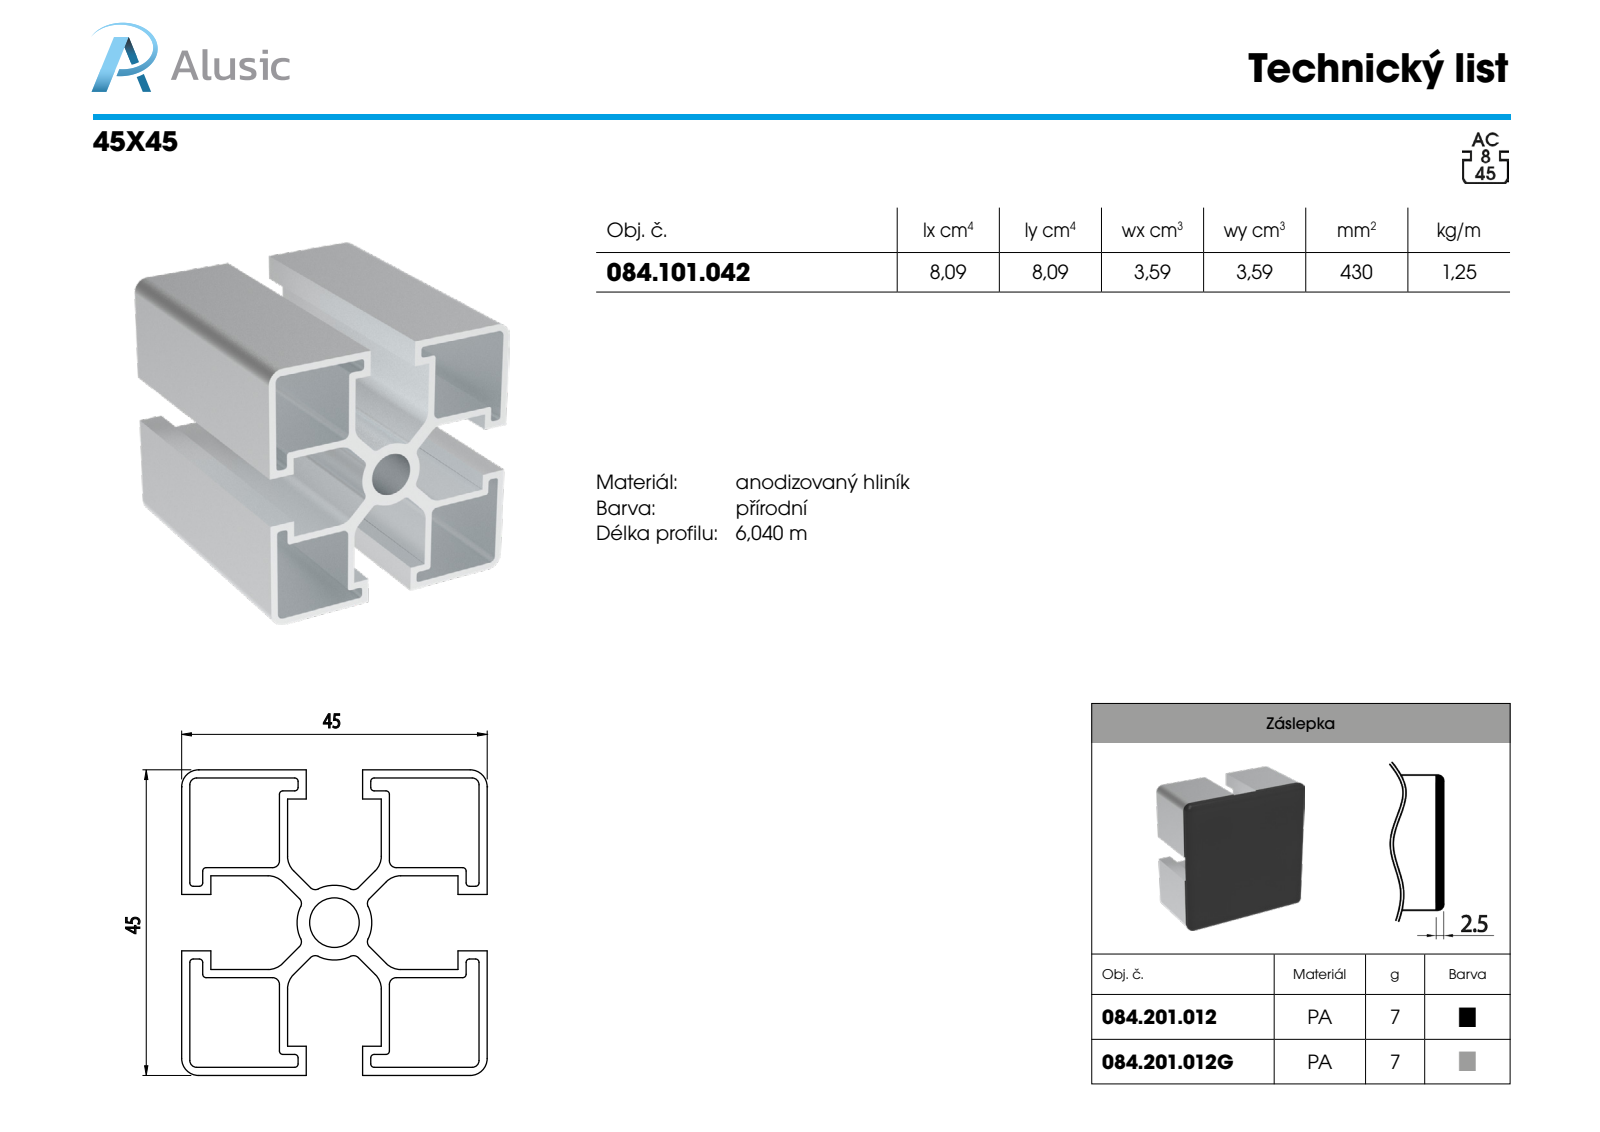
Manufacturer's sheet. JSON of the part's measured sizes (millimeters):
{"part_name": "084.101.042", "step_written_by": "SolidWorks 2018 (AUTOMOTIVE_DESIGN)", "units": "millimeters", "bodies": {"solids": 1, "faces": 135, "planar": 74, "cylindrical": 61, "other": 0}, "overall_size": [100, 45, 45], "volume_mm3": 42644, "surface_area_mm2": 62107, "round_holes": [[7.3, 1]], "partial_cylinders_radius": [[0.5, 24], [1, 16], [3, 8], [2.5, 4], [5.5, 1]], "face_to_face_distances": [1.2, 14.4, 29.4, 43.8, 30.6, 13.2, 15.6, 28.2, 15, 45]}
